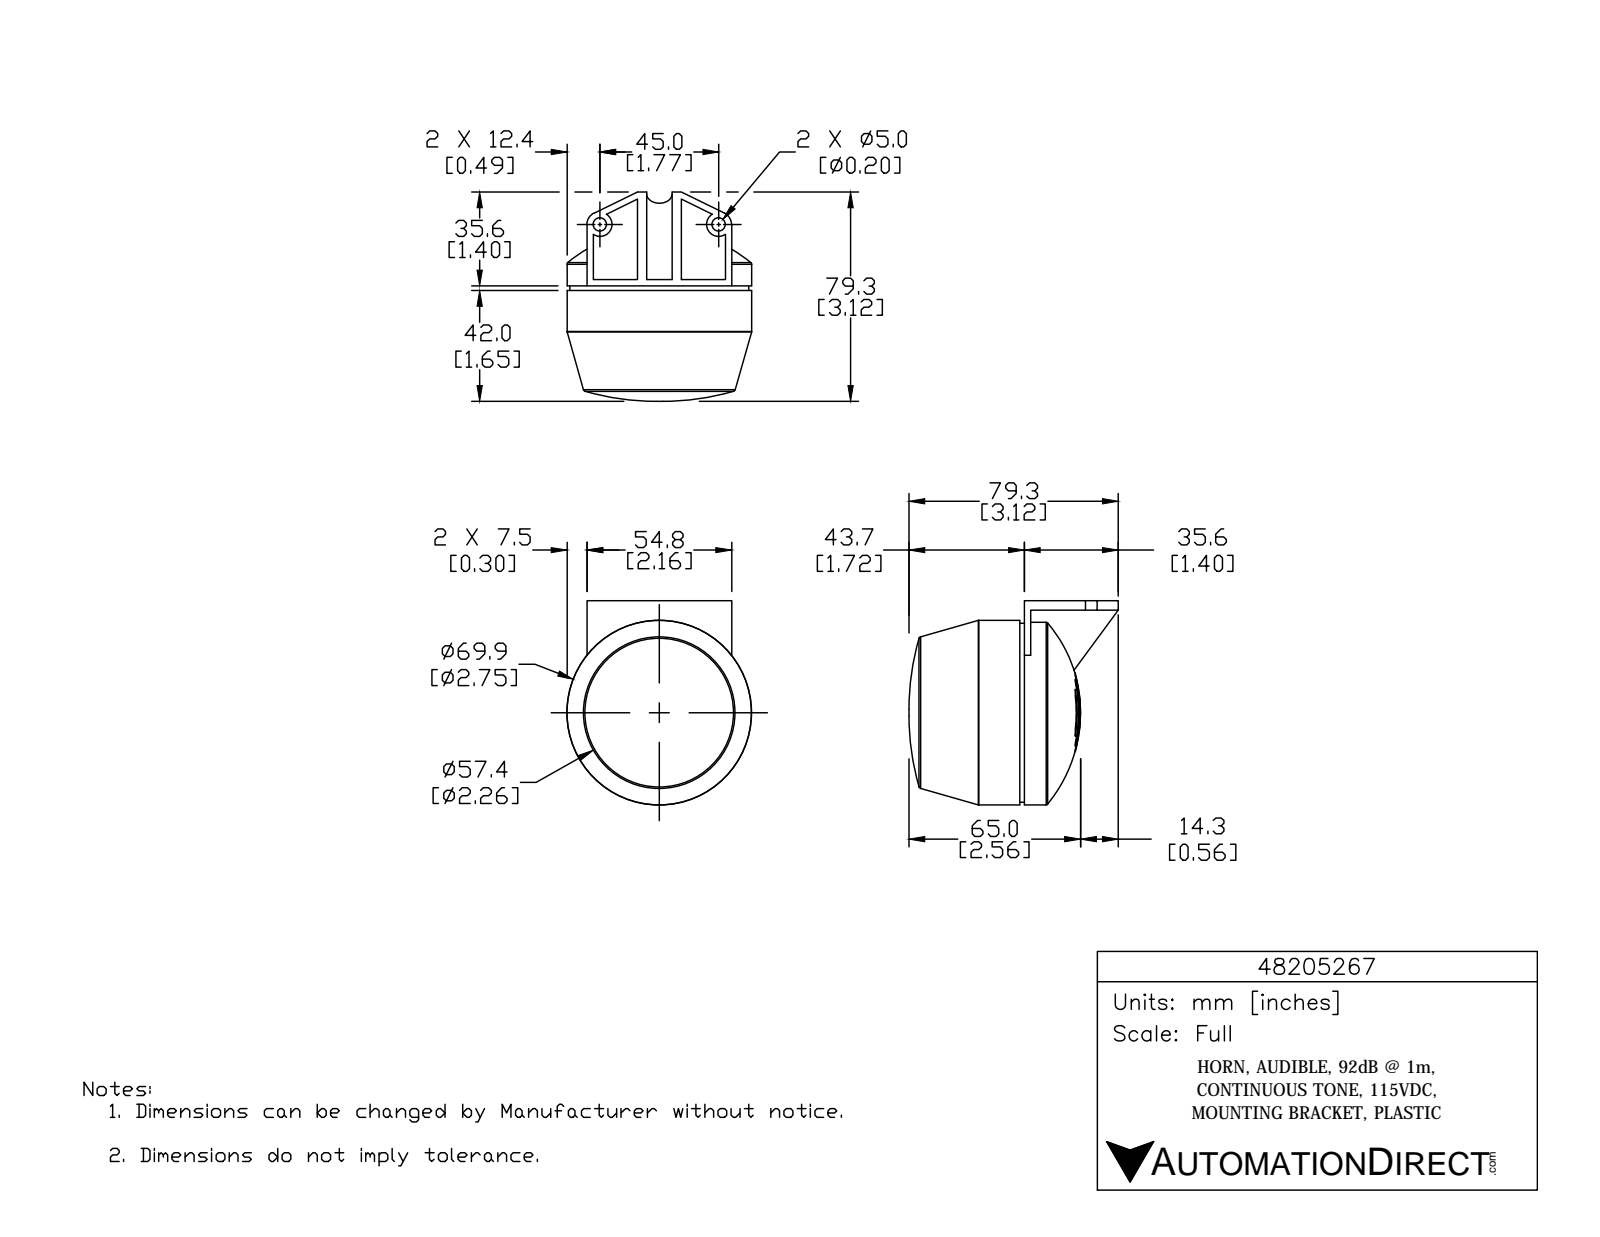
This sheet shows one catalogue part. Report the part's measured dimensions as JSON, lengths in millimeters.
{"part_name": "48234715_BODY; 482_3D Modell; 48234715_CAP", "step_written_by": "SolidWorks 2014 (AUTOMOTIVE_DESIGN)", "units": "millimeters", "bodies": {"solids": 2, "faces": 110, "planar": 49, "cylindrical": 38, "other": 23}, "overall_size": [79.2, 77.3, 69.9], "volume_mm3": 50460, "surface_area_mm2": 43940, "round_holes": [[5, 2], [62.2, 1], [65.5, 1]], "round_bosses_or_shafts": [[69.9, 1], [67.7, 1], [65.2, 1]], "partial_cylinders_radius": [[4.6, 2], [4.9, 2], [4.8, 1], [14.7, 1]], "face_to_face_distances": [2.6, 1.7, 3.6, 1, 4.2, 2.4, 4.1, 1.7, 12.7, 15.8], "hole_center_spacings": [45]}
